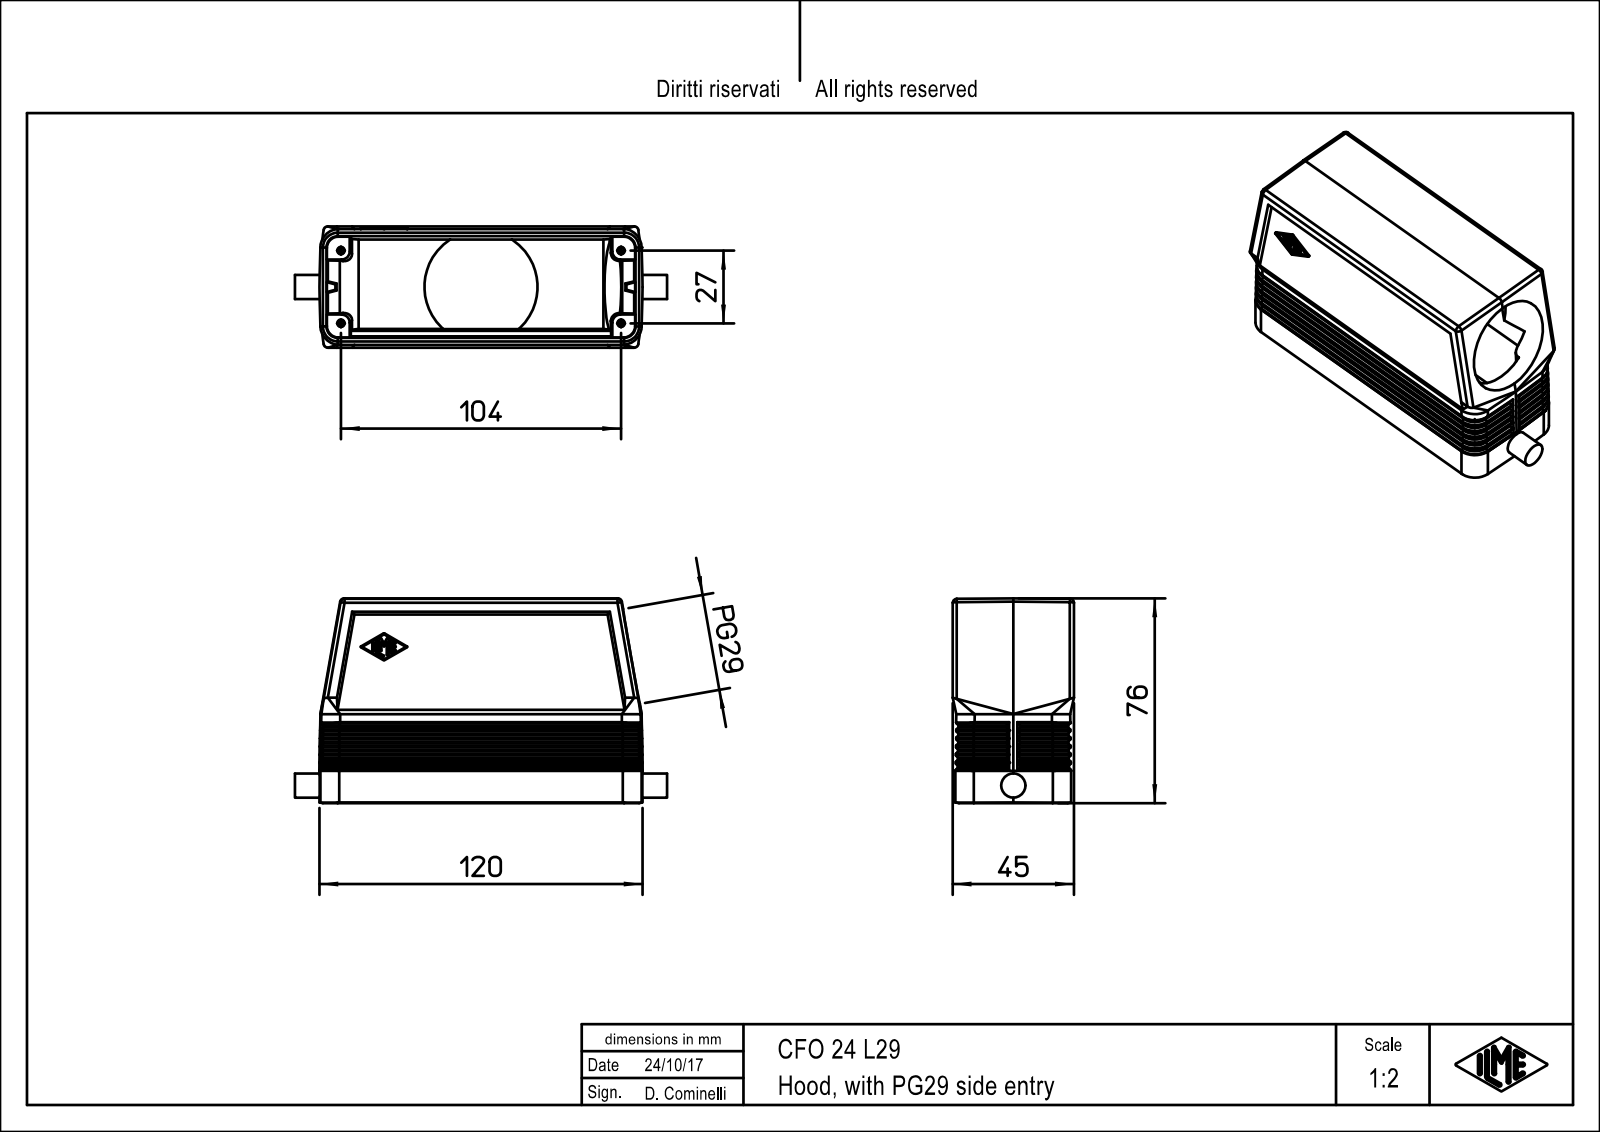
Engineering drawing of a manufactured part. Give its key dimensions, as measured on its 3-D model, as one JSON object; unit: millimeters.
{"part_name": "CFO_24_L29", "step_written_by": "PTC Creo Elements/Direct Modeling 19.0E 27-Jun-2016 (C) Parametric Technology GmbH (AUTOMOTIVE_DESIGN)", "units": "millimeters", "bodies": {"solids": 1, "faces": 513, "planar": 238, "cylindrical": 139, "other": 136}, "overall_size": [138.2, 76, 45], "volume_mm3": 104311, "surface_area_mm2": 53959, "round_holes": [[35.7, 1]], "round_bosses_or_shafts": [[9, 1]], "partial_cylinders_radius": [[0.5, 78], [0.33, 15], [1.5, 10], [7, 8], [3, 4], [4.2, 4], [0.17, 3], [0.67, 1]], "face_to_face_distances": [43, 2.01, 2, 4, 3.2, 1, 44, 6, 8.45, 6.01]}
